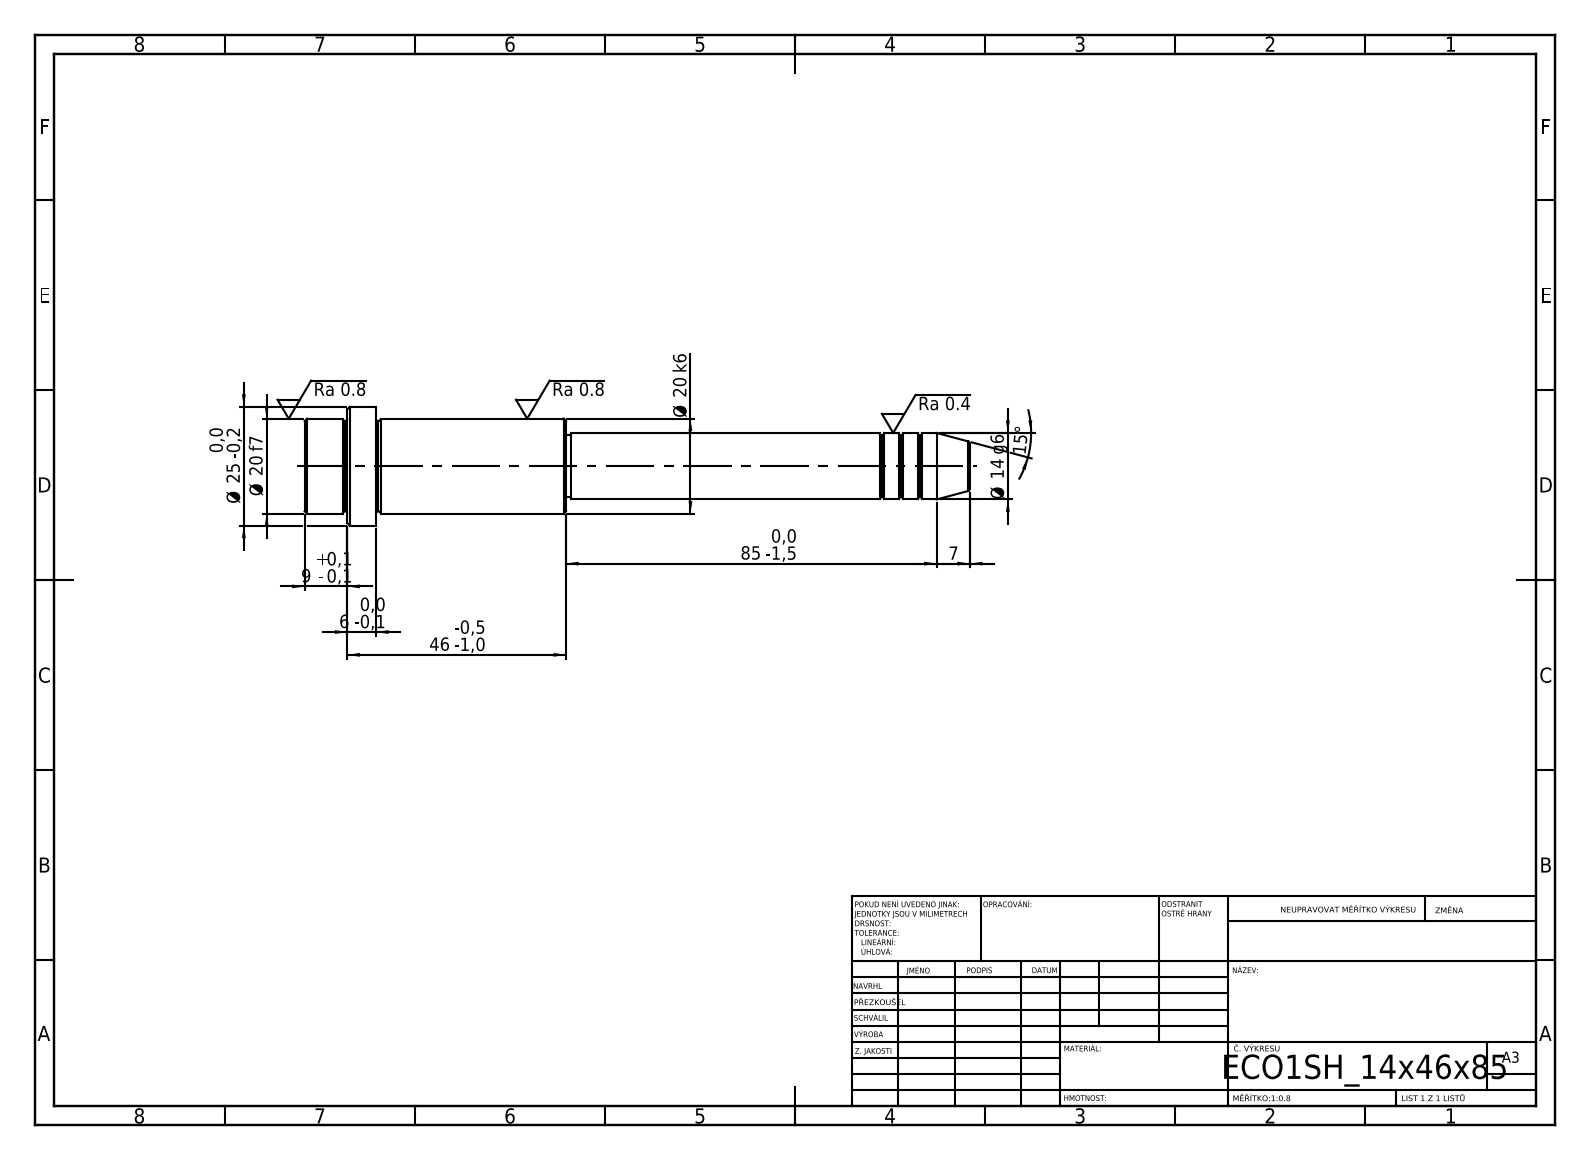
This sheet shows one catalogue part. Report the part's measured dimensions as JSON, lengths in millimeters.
{"step_written_by": "SolidWorks 2019 (CONFIG_CONTROL_DESIGN)", "units": "millimeters", "bodies": {"solids": 1, "faces": 52, "planar": 6, "cylindrical": 16, "other": 30}, "overall_size": [140, 25, 25], "volume_mm3": 31015, "surface_area_mm2": 8273, "round_bosses_or_shafts": [[25, 1], [20, 1], [14, 1], [13, 1]], "face_to_face_distances": [15, 40, 55, 46, 6, 9, 85, 125, 131, 140]}
